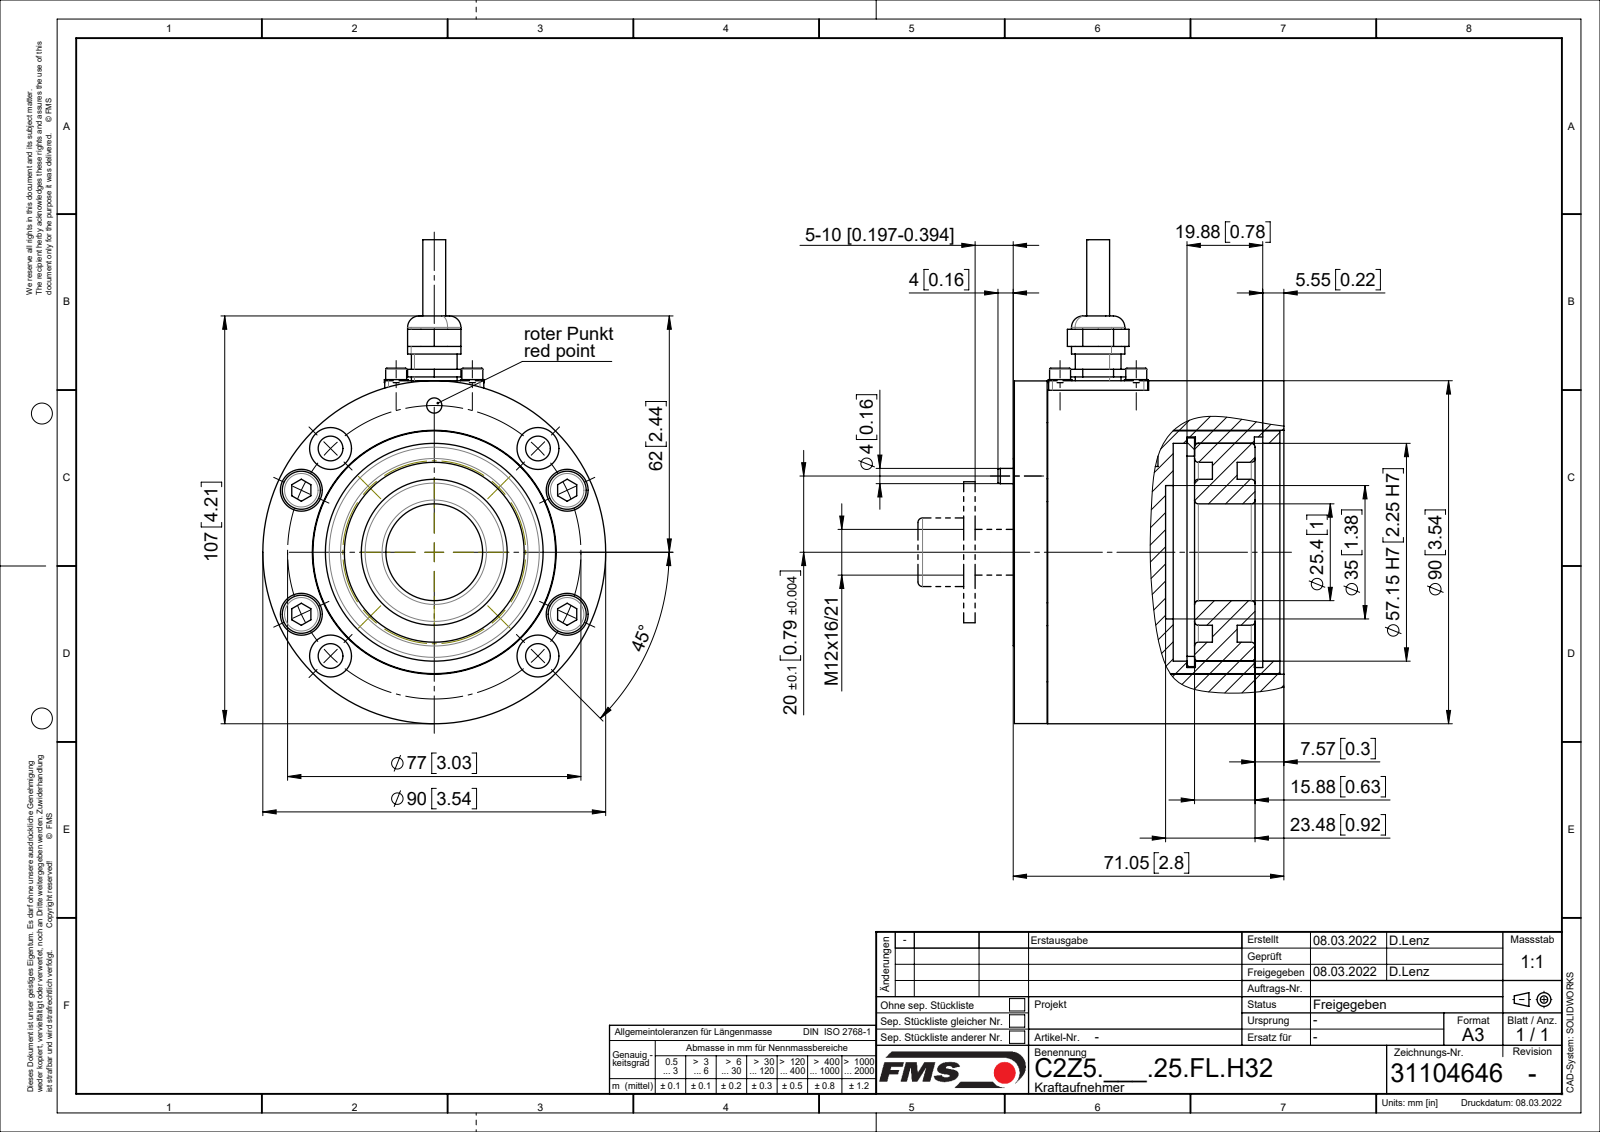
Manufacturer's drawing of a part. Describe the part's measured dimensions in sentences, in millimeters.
The part is named "Spannstift_ISO13337_D04x10; 31104496_stp_01; Federringe_DIN127A_M03; Si-Ring DIN472_D57.15 (+8 more)". Its 3-D file was written by "SolidWorks 2018 (CONFIG_CONTROL_DESIGN)". It is 23 solids with 525 faces: 201 planar, 228 cylindrical and 96 other. Overall it measures 127 by 96.05 by 90 millimeters. Its volume is 307 821 cubic millimeters and its surface area 120 518 square millimeters. Round holes: 8 of diameter 6.5, 8 of diameter 11, 6 of diameter 2.5, 4 of diameter 3.1, 4 of diameter 3.4, 4 of diameter 5, 4 of diameter 7, 2 of diameter 4, 1 of diameter 3, 1 of diameter 6, 1 of diameter 10.2, 1 of diameter 12.2. Round bosses or shafts: 4 of diameter 10, 4 of diameter 6.2, 4 of diameter 6, 4 of diameter 5.5, 4 of diameter 3, 2 of diameter 12, 1 of diameter 90, 1 of diameter 89.9. Partial cylindrical surfaces (rounded edges, fillets, slot ends): 4 of radius 0.1, 4 of radius 1, 2 of radius 0.5, 2 of radius 4.16, 2 of radius 5, 1 of radius 23.2, 1 of radius 26.29. The main face-to-face distances are 6, 33.05, 32, 38, 8.6, 29.1, 37.7, 5.7, 2.9, 28.95. The hole center spacings are 20, 38.5, 13.37, 14.14, 38.49, 44.16, 54.44, 63.07.
